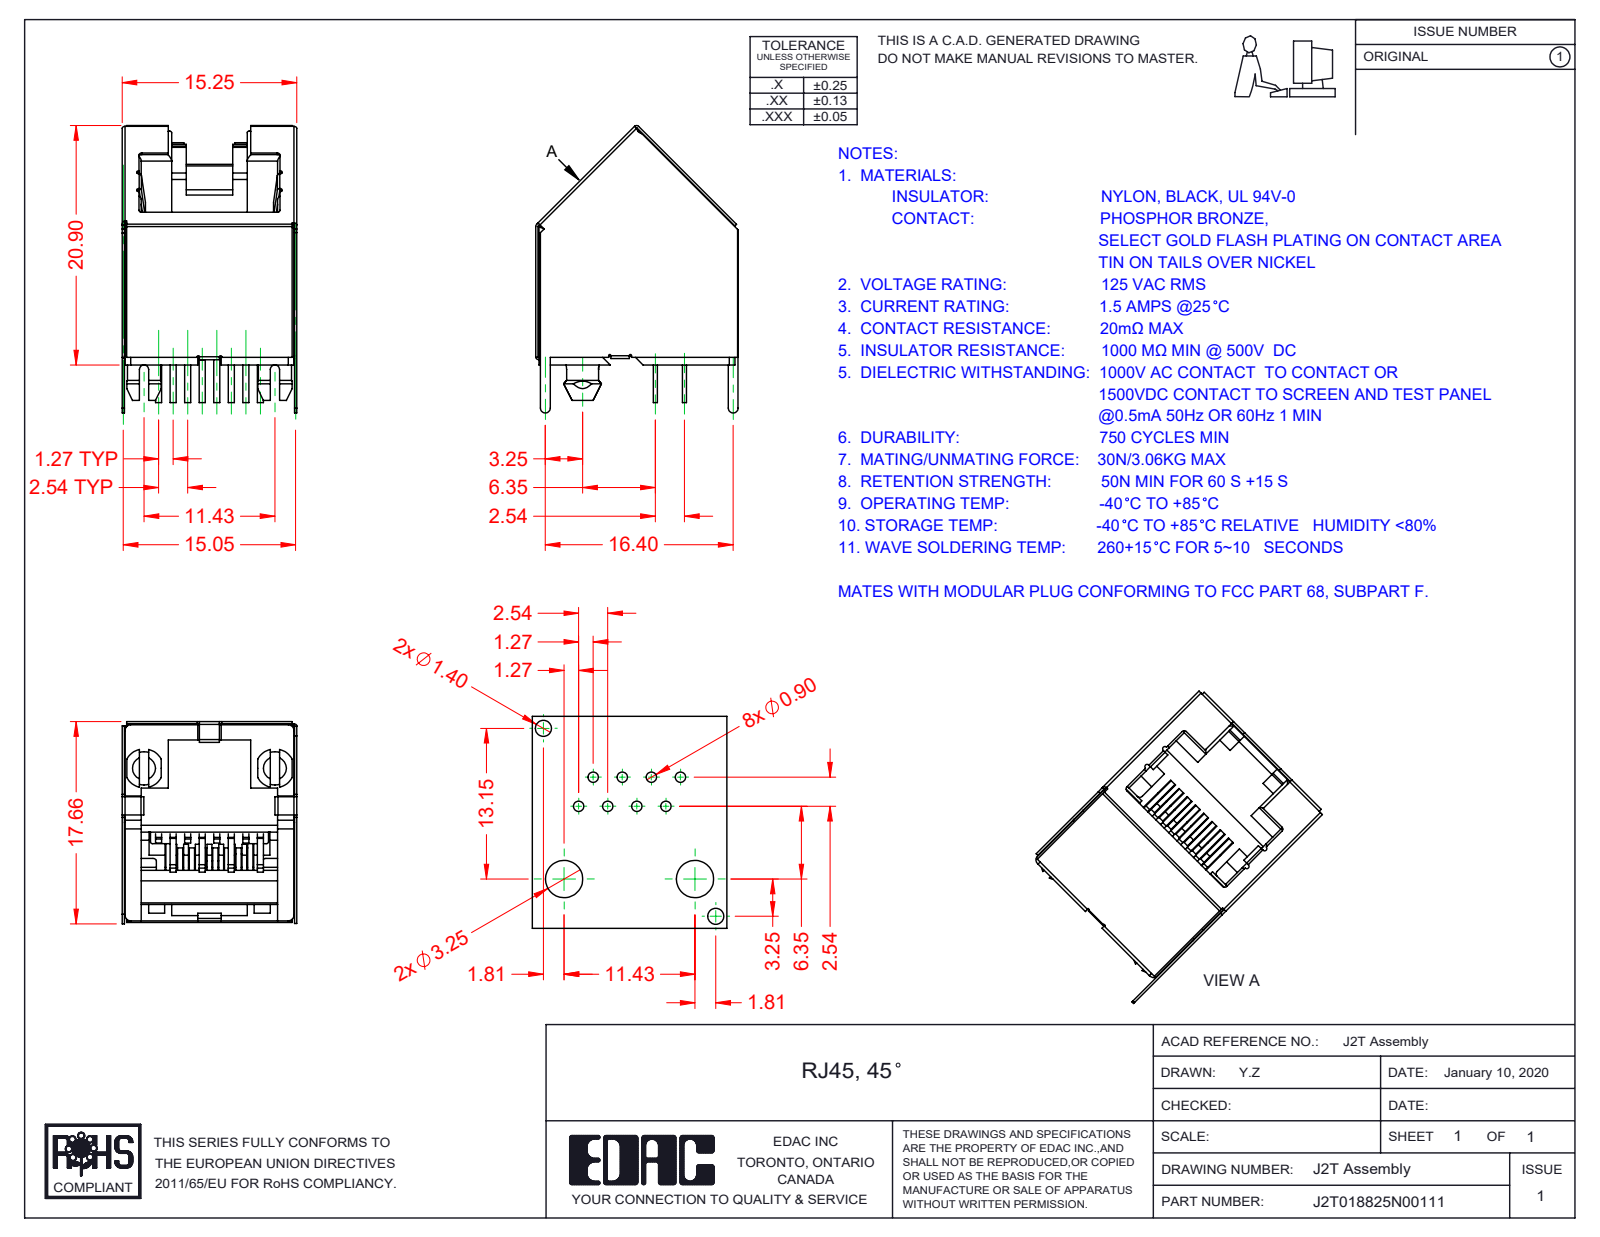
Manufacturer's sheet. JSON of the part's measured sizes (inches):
{"part_name": "2T Contacts; 2T Contact Lock; 2T Shell; 2T Insulator (+1 more)", "step_written_by": "SolidWorks 2016 (CONFIG_CONTROL_DESIGN)", "units": "inches", "bodies": {"solids": 11, "faces": 631, "planar": 447, "cylindrical": 161, "other": 23}, "overall_size": [0.988, 0.695, 0.6], "volume_in3": 0.12, "surface_area_in2": 8.026, "round_bosses_or_shafts": [[0.114, 2]], "partial_cylinders_radius": [[0.02, 21], [0.039, 16], [0.008, 12], [0.01, 10], [0.057, 8], [0.06, 8], [0.004, 5], [0.012, 3]], "face_to_face_distances": [0.592, 0.056, 0.525, 0.583, 0.591, 0.6, 0.584, 0.59, 0.582, 0.581]}
